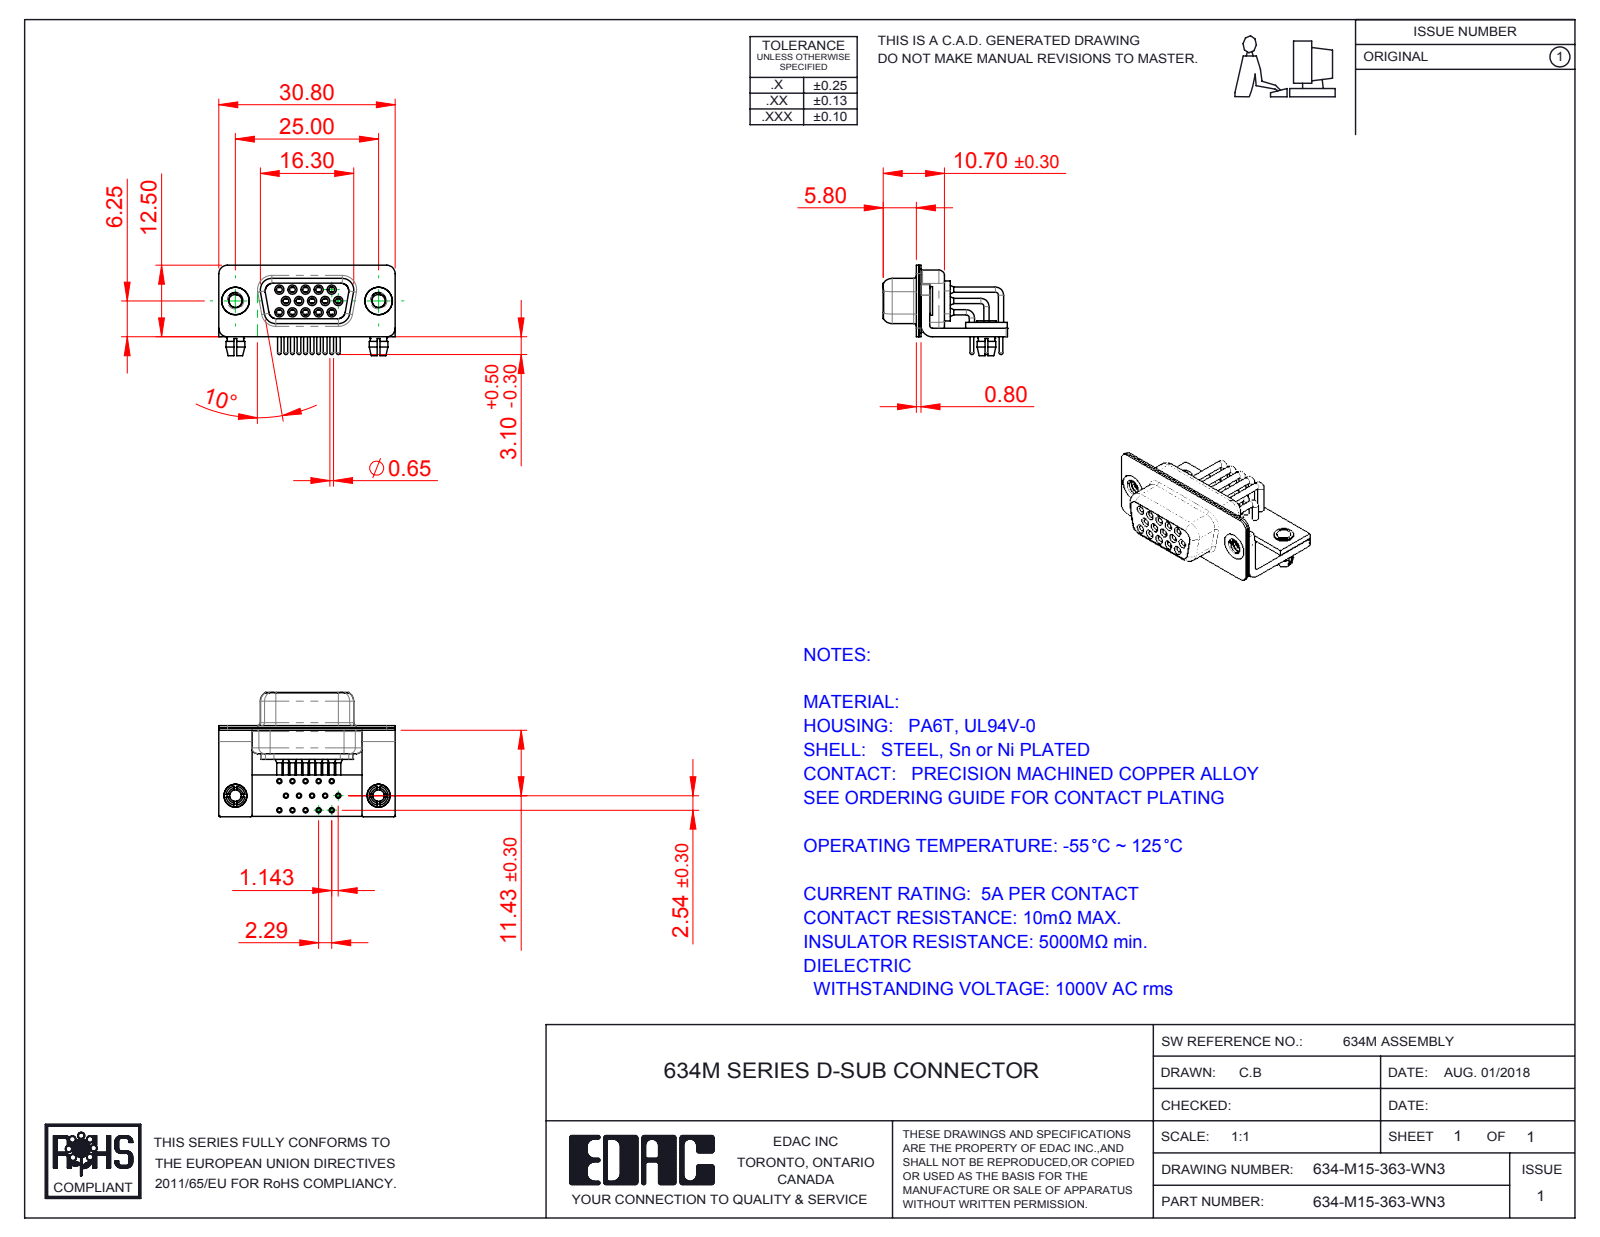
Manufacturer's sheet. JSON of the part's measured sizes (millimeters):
{"part_name": "634M 4-40 Threaded Rivet_Stabilizer; 634M Contact Row 3; 634M Contact Row 2; 634M Contact Row 1 (+7 more)", "step_written_by": "SolidWorks 2016 (CONFIG_CONTROL_DESIGN)", "units": "millimeters", "bodies": {"solids": 25, "faces": 1246, "planar": 366, "cylindrical": 566, "other": 314}, "overall_size": [30.8, 21.7, 15.8], "volume_mm3": 2262, "surface_area_mm2": 7060, "round_holes": [[2, 17], [0.9, 15], [1, 15], [1.1, 15], [1.7, 15], [1.8, 15], [2.26, 2], [2.5, 2], [3.2, 2], [4, 2], [4.8, 2]], "round_bosses_or_shafts": [[1.6, 15], [1.5, 15], [0.9, 15], [0.65, 15], [5, 2], [4.9, 2], [4, 2], [3.4, 2]], "partial_cylinders_radius": [[0.25, 16], [1.5, 16], [2, 13], [1.35, 8], [1.6, 8], [0.5, 5], [0.6, 4], [0.65, 4]], "face_to_face_distances": [0.4, 1.5, 0.8, 1, 2.3, 1.9, 9.35, 2.5, 1.45, 8.95], "hole_center_spacings": [2.29, 2.28, 4.57, 3.96, 4.27, 2.78, 6.05, 6.86]}
